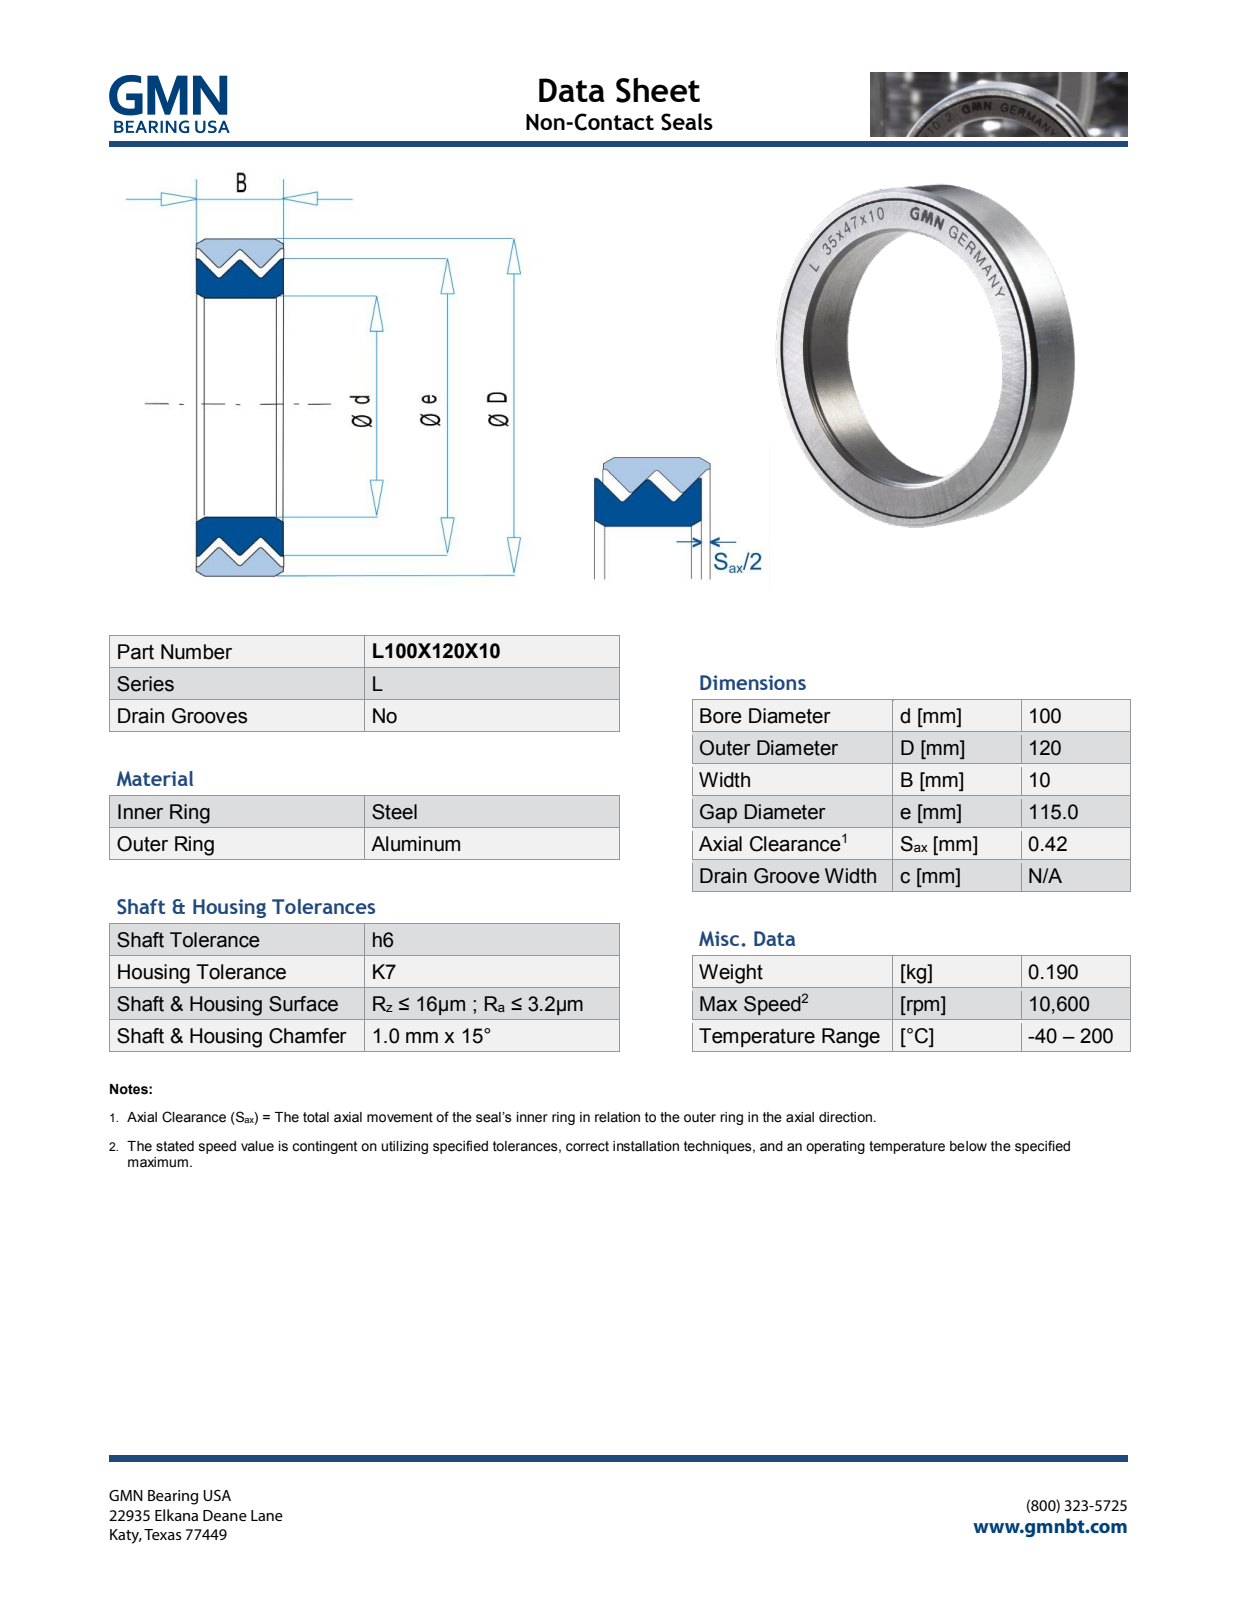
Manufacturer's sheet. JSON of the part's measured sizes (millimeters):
{"part_name": "L100X120X10_PRT", "step_written_by": "PRO/ENGINEER BY PARAMETRIC TECHNOLOGY CORPORATION, 2013150 (AUTOMOTIVE_DESIGN)", "units": "millimeters", "bodies": {"solids": 2, "faces": 604, "planar": 548, "cylindrical": 12, "other": 44}, "overall_size": [120, 120, 10.07], "volume_mm3": 33465, "surface_area_mm2": 22662, "round_holes": [[100, 1], [115.3, 1]], "round_bosses_or_shafts": [[120, 1], [115, 1]], "face_to_face_distances": [10, 10.07, 0.62, 4.92, 0.61, 0.63, 4.31, 3.69, 4.1, 4.93]}
